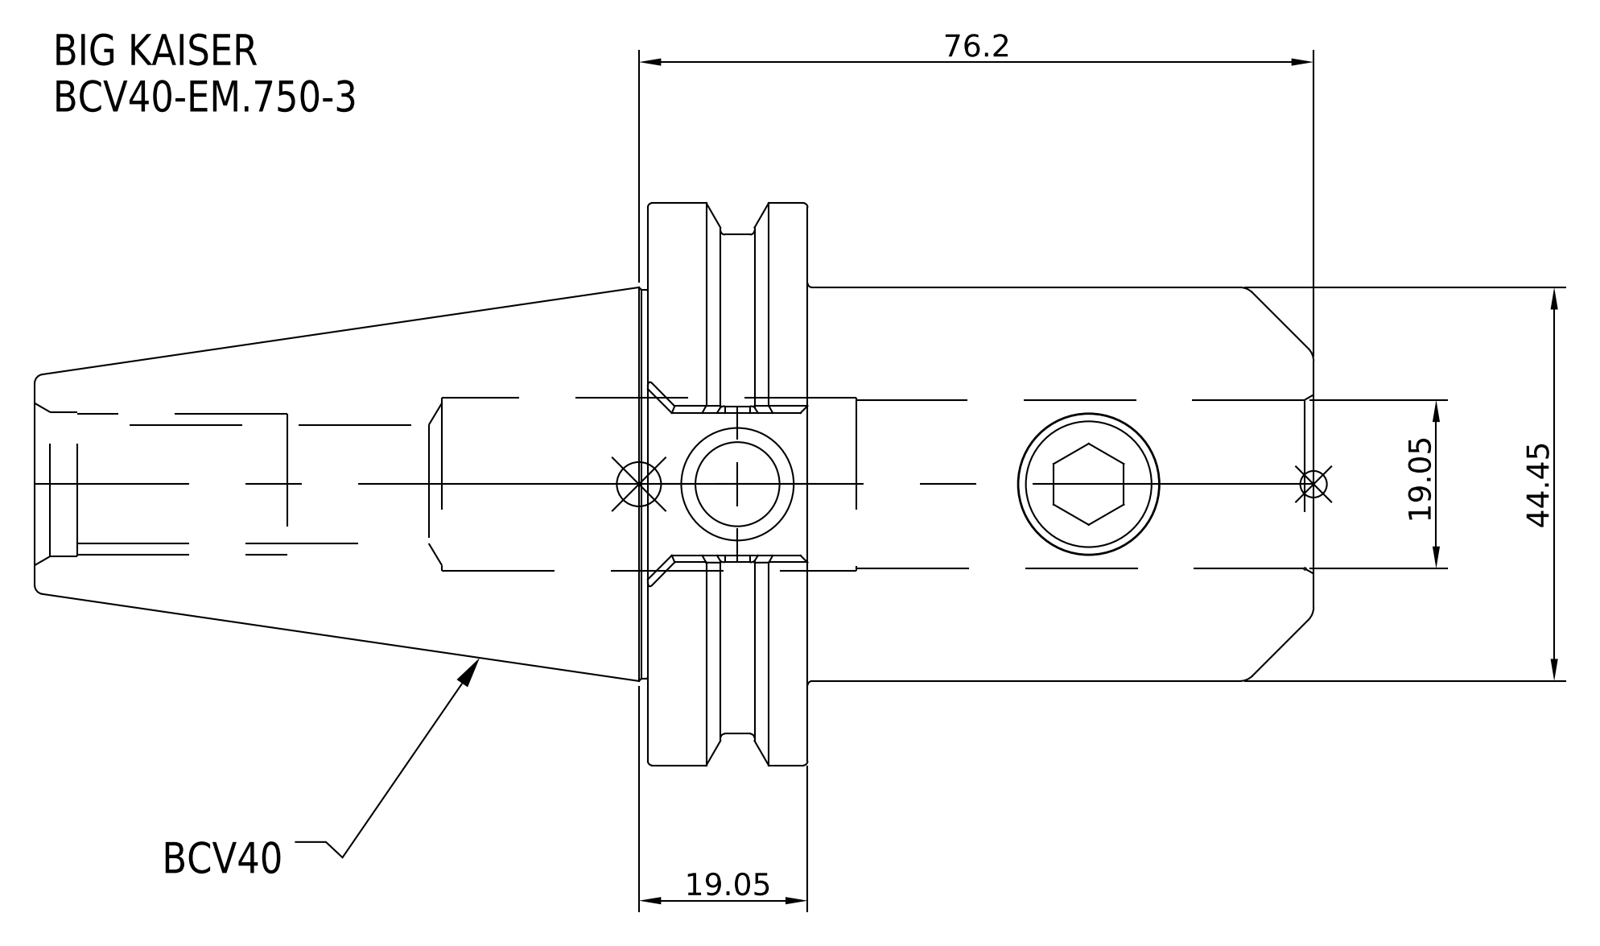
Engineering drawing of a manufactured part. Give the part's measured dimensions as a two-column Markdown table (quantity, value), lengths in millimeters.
| quantity | value |
| --- | --- |
| part name | BCV40-EM_750-3 |
| STEP written by | SolidWorks 2021 (CONFIG_CONTROL_DESIGN) |
| units | millimeters |
| bodies | 1 solid, 27 faces (7 planar, 12 cylindrical, 8 other) |
| overall size | 144.45 × 63.5 × 63.5 |
| volume | 194 299 mm³ |
| surface area | 27 010 mm² |
| round holes (diameter × count) | 19.05 × 1 |
| round bosses / shafts (diameter × count) | 63.5 × 1, 56.36 × 1, 44.45 × 1 |
| main face-to-face distances | 18.05, 87.3, 69.25, 57.15, 75.2, 144.45, 41.15, 16, 34.05, 103.3 |
